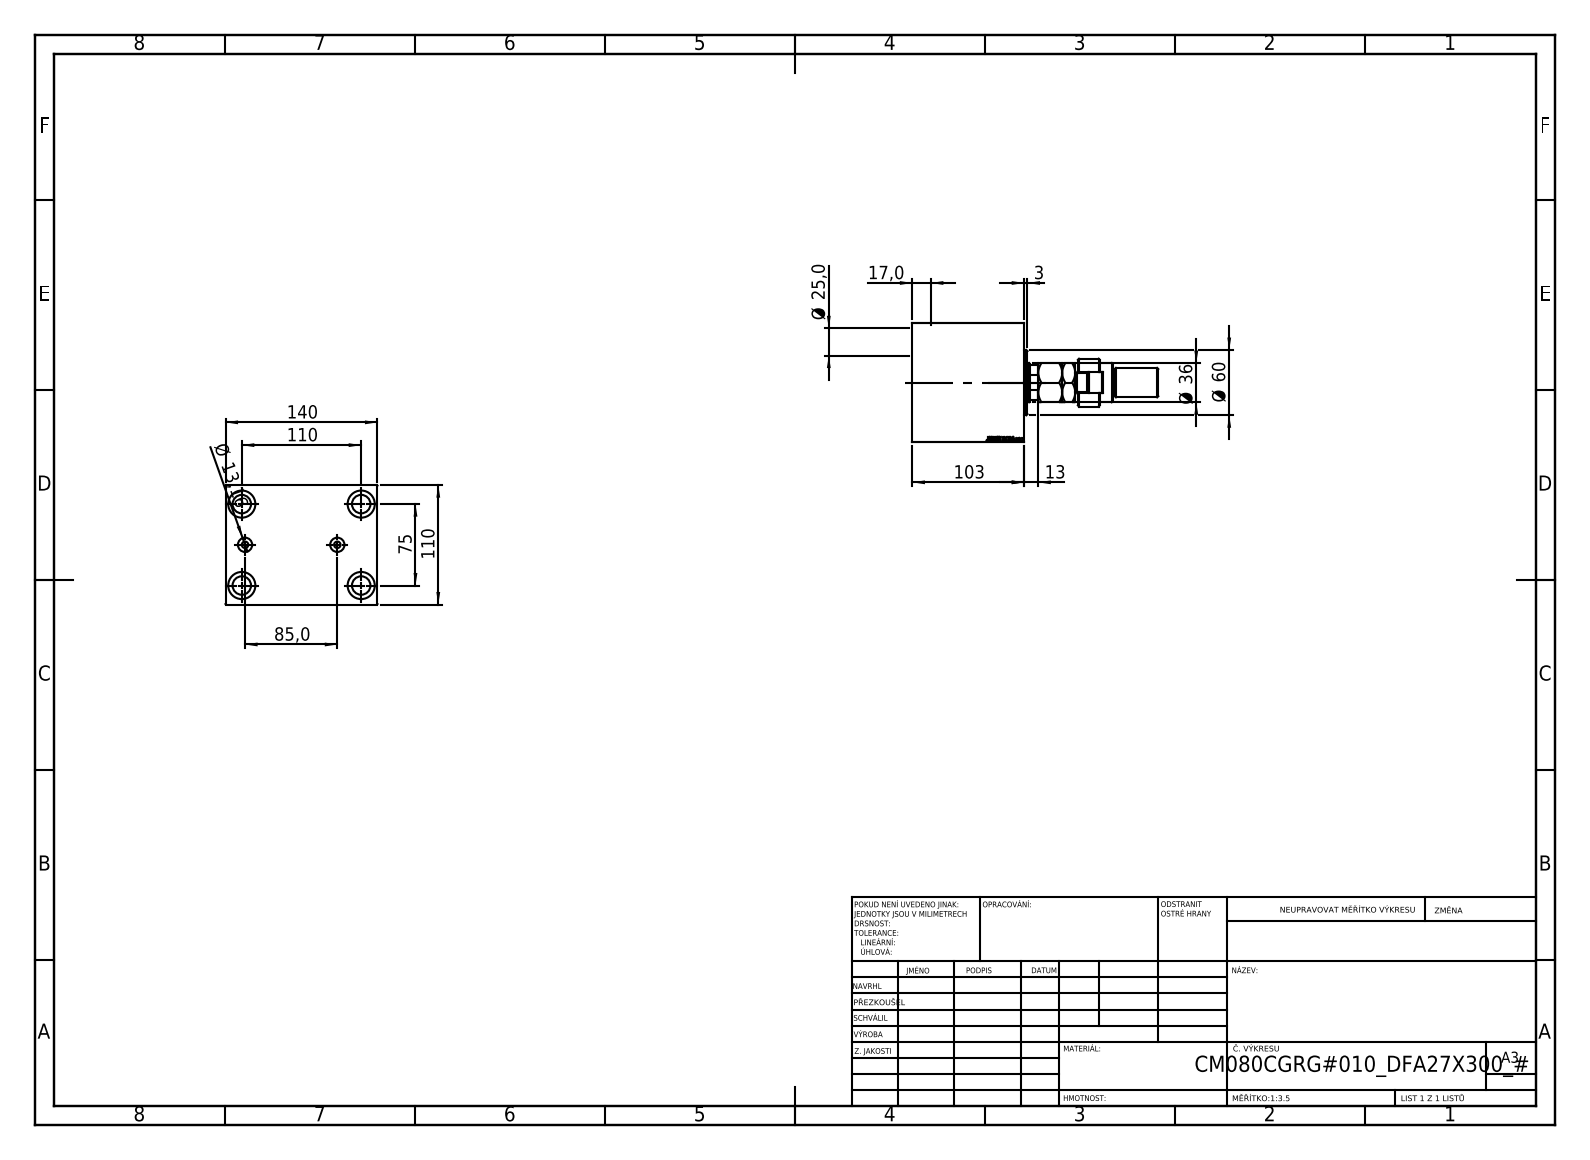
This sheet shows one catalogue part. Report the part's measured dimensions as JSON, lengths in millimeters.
{"part_name": "FEMALE_PART_FOR_DFA; V450CM_C_VCP; MFA; V450CM_C_Body (+1 more)", "step_written_by": "SolidWorks 2019 (CONFIG_CONTROL_DESIGN)", "units": "millimeters", "bodies": {"solids": 5, "faces": 945, "planar": 436, "cylindrical": 71, "other": 438}, "overall_size": [226.5, 140, 110], "volume_mm3": 1508000, "surface_area_mm2": 184423, "round_holes": [[17, 4], [25, 4], [6, 2], [13.16, 2], [25.5, 1], [39.5, 1], [80, 1], [82, 1], [87, 1]], "round_bosses_or_shafts": [[60, 1], [44, 1], [36, 1], [28, 1], [27, 1], [25, 1], [18, 1]], "partial_cylinders_radius": [[9.5, 1], [15, 1], [17.5, 1]], "face_to_face_distances": [110, 140, 52, 51, 103, 10, 21.6, 29.4, 81.4, 71.4], "hole_center_spacings": [66.57, 37.62, 43.48, 75, 95.66, 110, 113.38, 133.14]}
